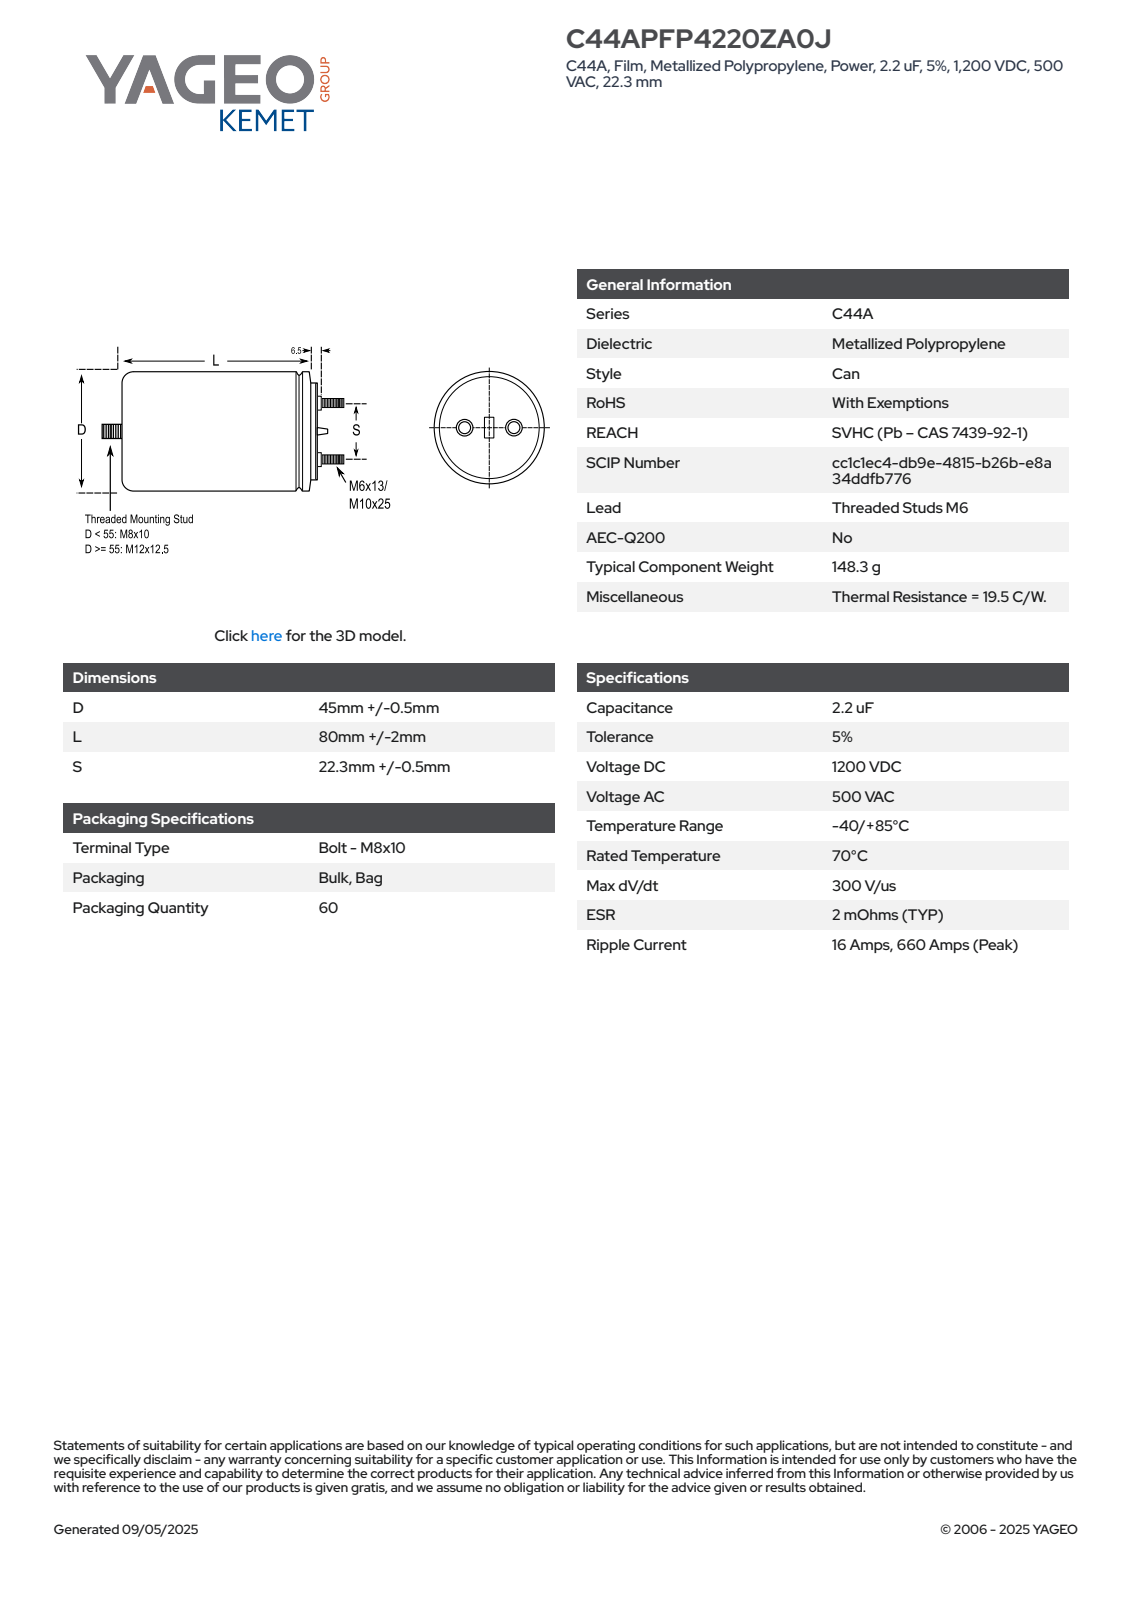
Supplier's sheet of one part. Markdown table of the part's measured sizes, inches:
| quantity | value |
| --- | --- |
| part name | CFP_C44A_45X80_D45.5L82S22.3 |
| STEP written by | SolidWorks 2014 (AUTOMOTIVE_DESIGN) |
| units | inches |
| bodies | 1 solid, 102 faces (29 planar, 34 cylindrical, 39 other) |
| overall size | 4.39 × 1.791 × 1.791 |
| volume | 8.464 in³ |
| surface area | 25.15 in² |
| round bosses / shafts (diameter × count) | 0.354 × 2, 0.236 × 2, 1.791 × 1, 1.405 × 1, 0.315 × 1 |
| partial cylindrical surfaces (radius × count) | 0.895 × 1 |
| main face-to-face distances | 3.425, 3.484, 0.059, 3.996, 0.571, 0.512, 0.394, 3.819, 3.878, 4.39 |
